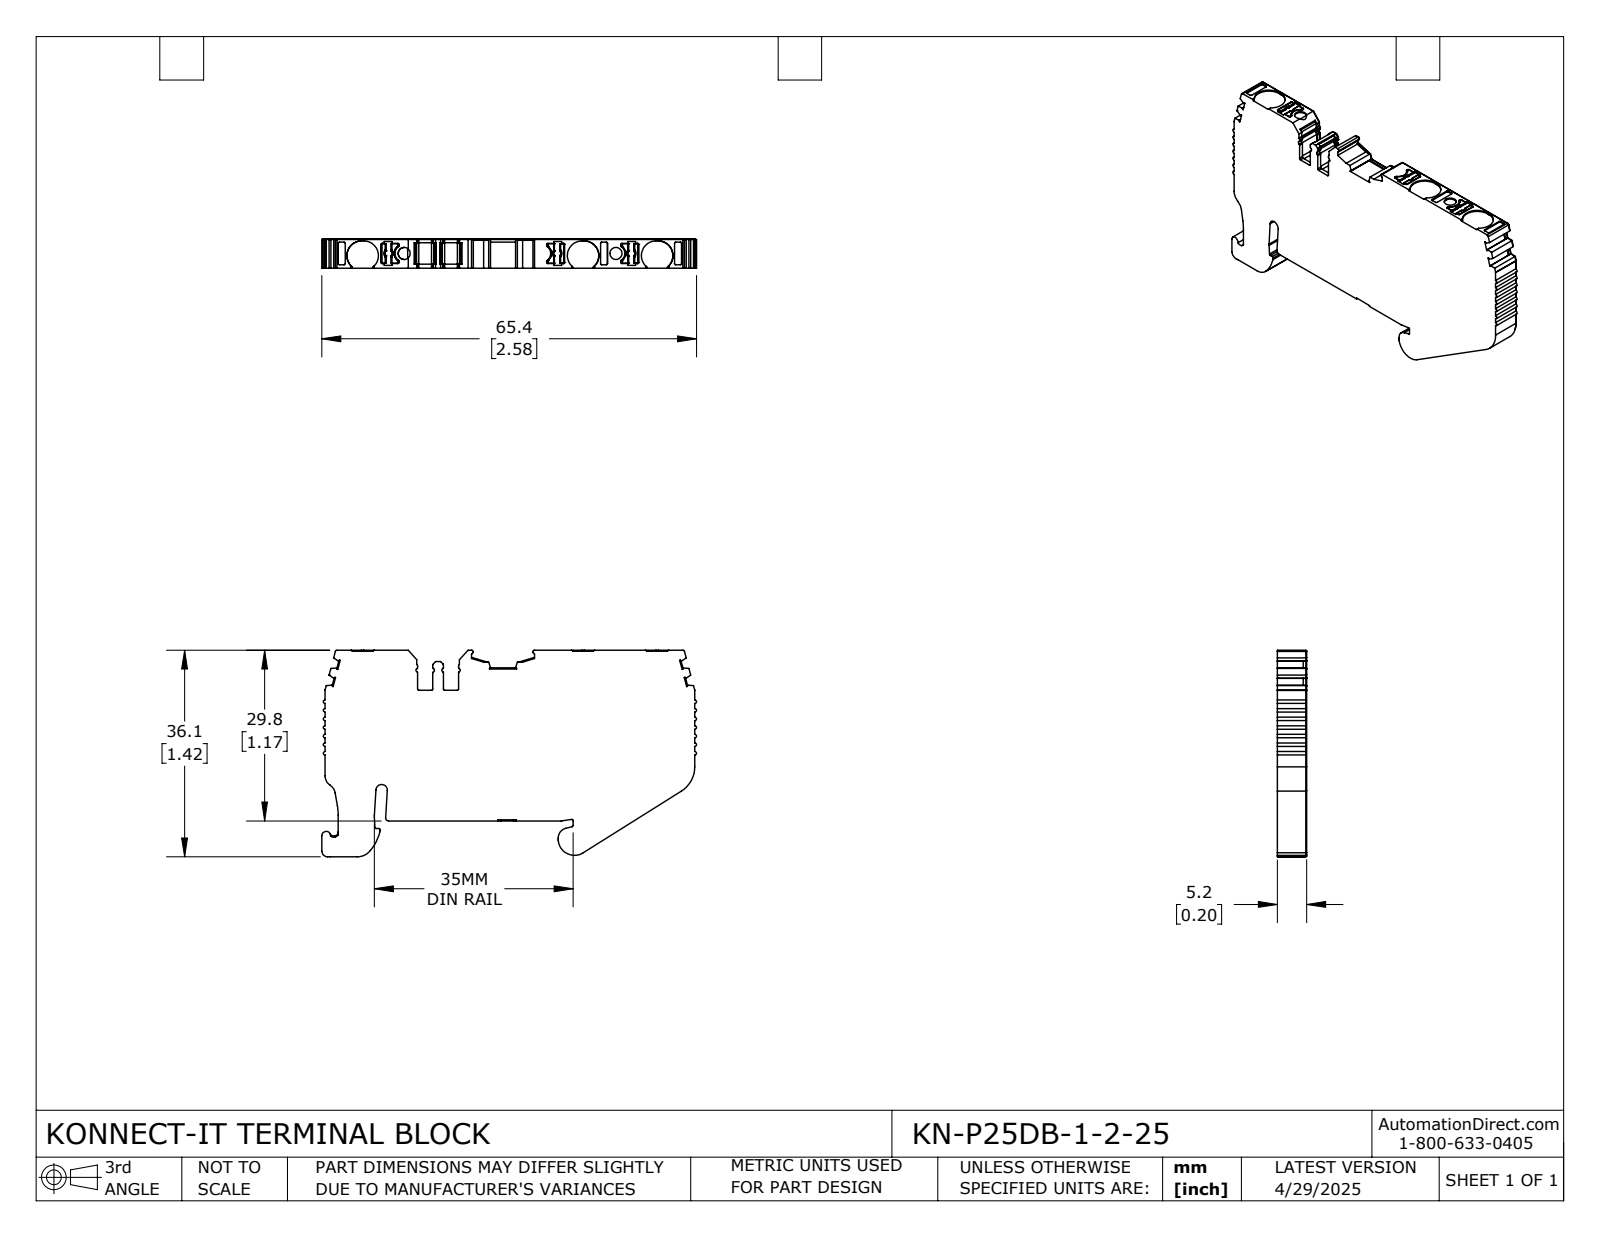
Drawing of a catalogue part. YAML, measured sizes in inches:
part_name: "KN-P25DB-1-2-25"
step_written_by: "SolidWorks 2024 (CONFIG_CONTROL_DESIGN)"
units: inches
bodies: {solids: 1, faces: 655, planar: 345, cylindrical: 259, other: 51}
overall_size: [2.576, 1.42, 0.203]
volume: 0.584
surface_area: 7.967
round_holes:
  - {diameter: 0.083, count: 2}
partial_cylinders:
  - {radius: 0.008, count: 66}
  - {radius: 0.012, count: 39}
  - {radius: 0.004, count: 19}
  - {radius: 0.02, count: 18}
  - {radius: 0.006, count: 12}
  - {radius: 0.016, count: 9}
  - {radius: 0.1, count: 6}
  - {radius: 0.039, count: 3}
face_to_face_distances: [0.203, 1.166, 1.174, 2.543, 0.177, 0.197, 0.246, 1.412, 0.079, 1.42]
hole_center_spacings: [1.456]
